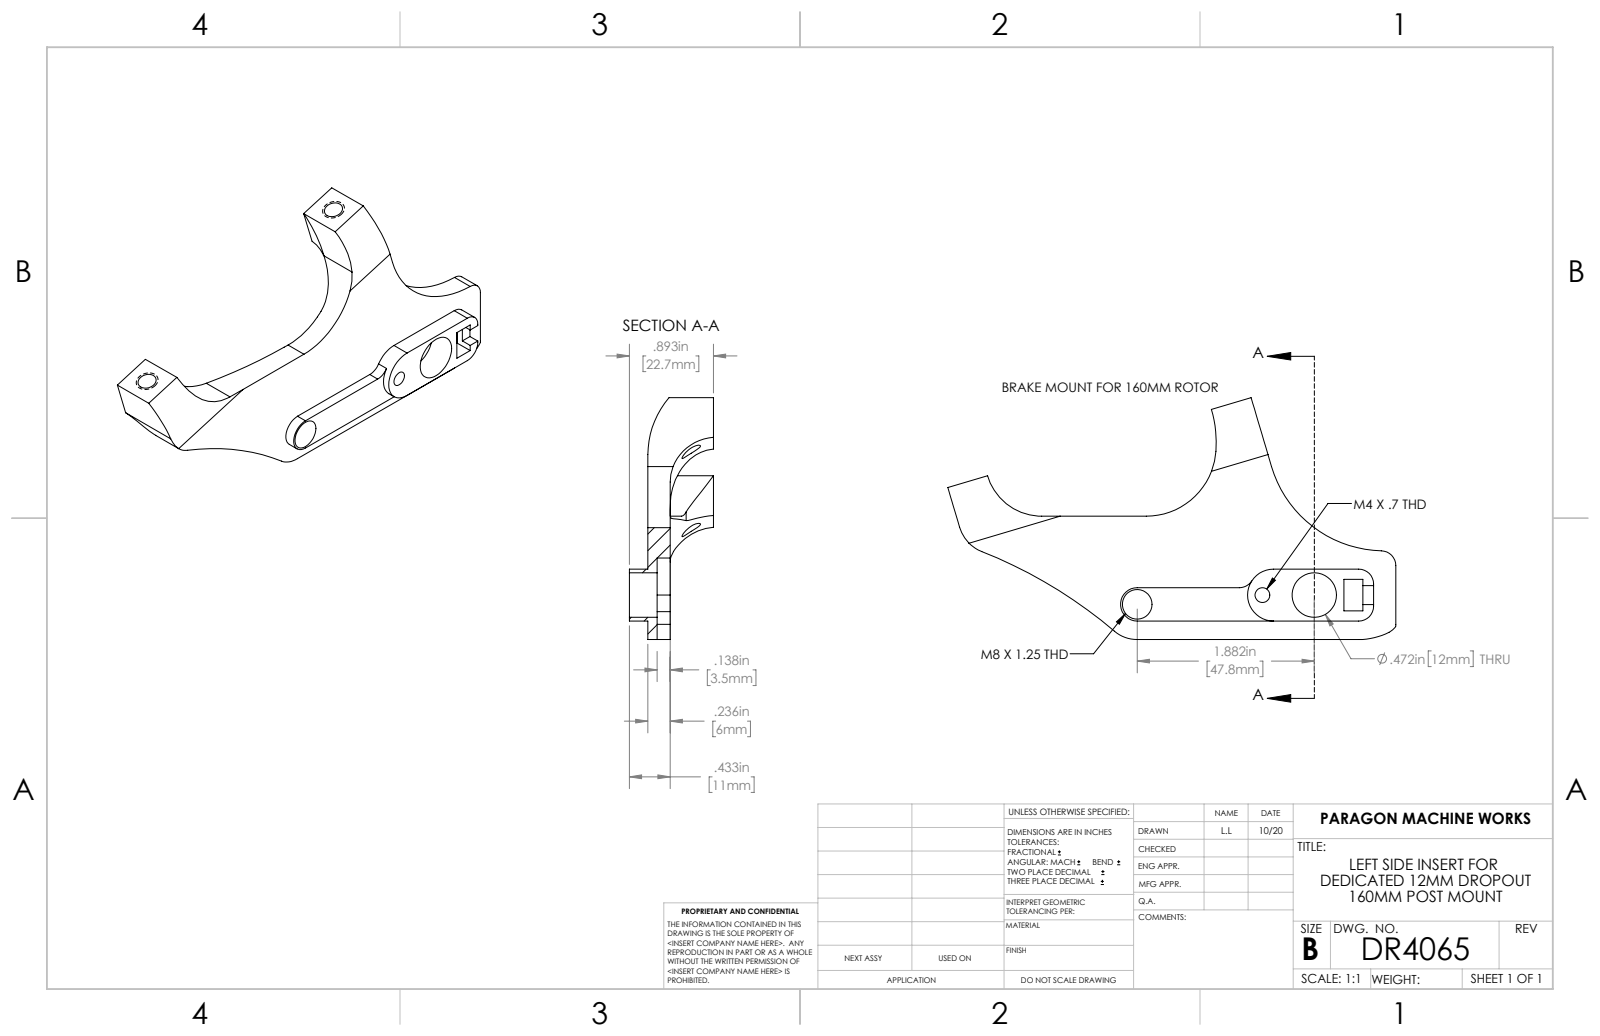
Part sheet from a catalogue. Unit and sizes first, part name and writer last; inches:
Units: inches
Overall size (bounding box): 4.76 × 2.569 × 0.893
Round holes (diameter × count): ⌀0.197 ×2, ⌀0.157 ×1, ⌀0.315 ×1, ⌀0.472 ×1
Partial cylindrical surfaces — rounded edges, fillets, slot ends (radius × count): R0.157 ×5, R0.394 ×2, R1.25 ×2, R0.177 ×1, R0.206 ×1, R0.276 ×1, R0.3 ×1, R0.374 ×1
Main face-to-face distances: 0.236, 0.197, 0.354, 0.079, 0.138, 0.098, 0.118, 0.433, 0.295, 0.217
Hole centre spacings: 0.551, 1.334, 1.884, 2.921
Volume: 1.561 in³ · Surface area: 18.31 in²
Bodies: 1 solid, 67 faces (31 planar, 36 cylindrical, 0 other)
Part name (STEP PRODUCT): DR4065
STEP written by: SolidWorks 2021 (AUTOMOTIVE_DESIGN)
